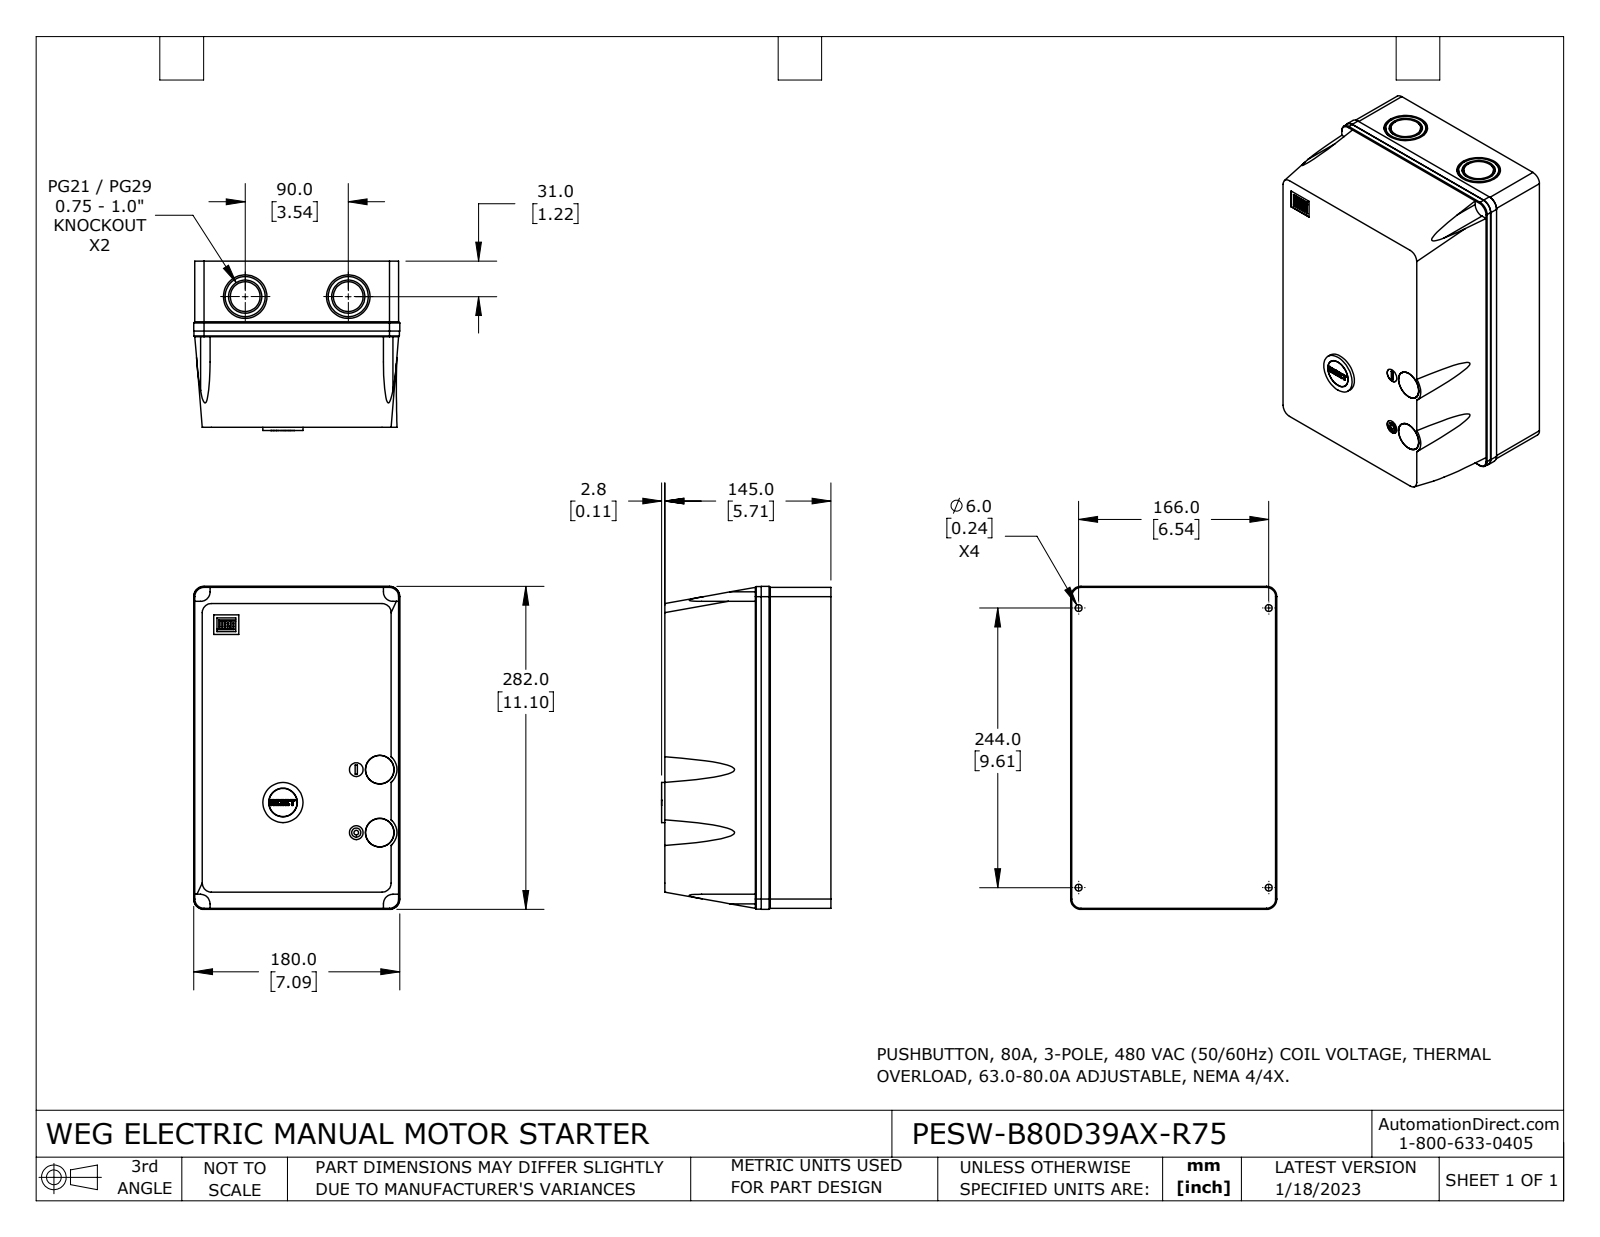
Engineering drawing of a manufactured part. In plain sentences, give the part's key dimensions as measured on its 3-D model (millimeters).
The part is named "PESW-B80D39AX-R75". Its 3-D file was written by "SolidWorks 2021 (CONFIG_CONTROL_DESIGN)". It is 3 solids with 286 faces: 130 planar, 144 cylindrical and 12 other. Overall it measures 282 by 180 by 147.9 millimeters. Its volume is 7 014 000 cubic millimeters and its surface area 232 257 square millimeters. Round holes: 4 of diameter 6, 3 of diameter 25, 2 of diameter 12, 2 of diameter 29, 2 of diameter 38, 1 of diameter 4, 1 of diameter 30.5. Round bosses or shafts: 3 of diameter 35, 2 of diameter 26, 2 of diameter 24.8, 1 of diameter 30.3, 1 of diameter 24.6, 1 of diameter 14, 1 of diameter 8. Partial cylindrical surfaces (rounded edges, fillets, slot ends): 34 of radius 0.1, 4 of radius 8, 4 of radius 8.3, 4 of radius 8.7, 4 of radius 9, 1 of radius 1.6. The main face-to-face distances are 145, 178, 280, 1, 0.7, 179, 179.7, 178.7, 281, 180. The hole center spacings are 20.5, 55, 58.7, 166, 244, 295.11, 49.14, 57.14.
